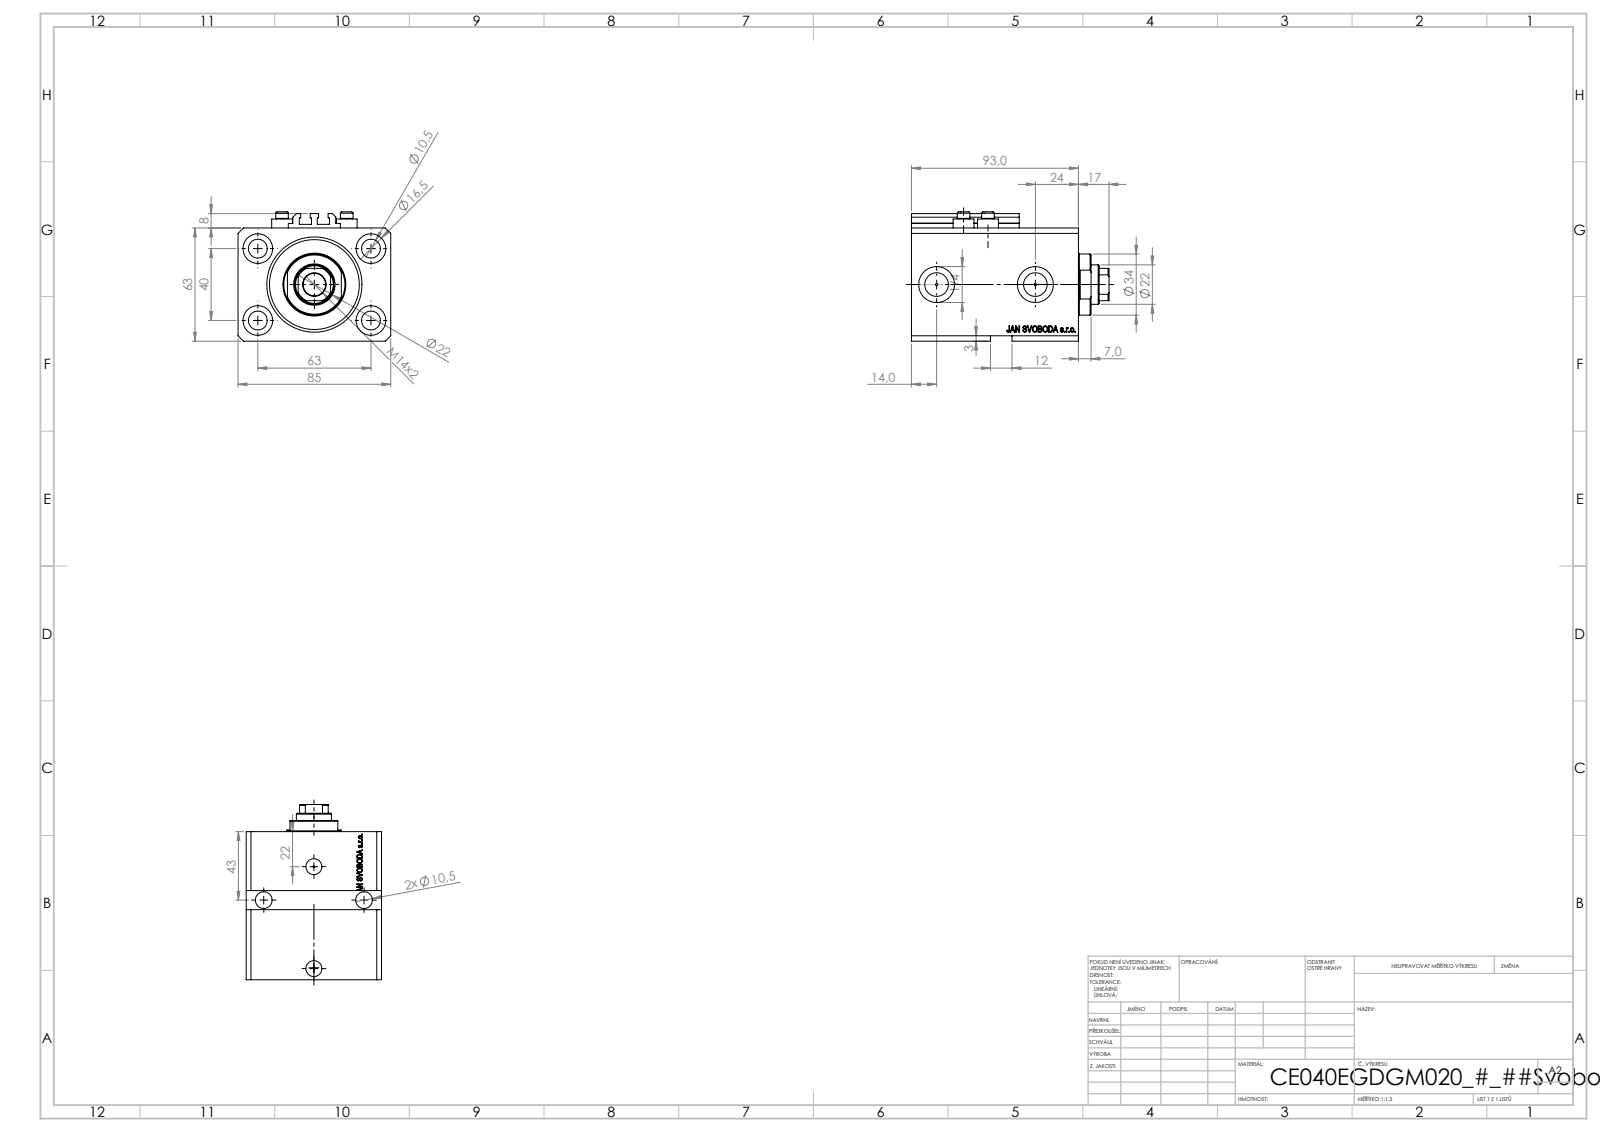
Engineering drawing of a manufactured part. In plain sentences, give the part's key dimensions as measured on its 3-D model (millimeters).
The part is named "V250CE_E_Body; V250CE_C_VCP; V250CE_VC_E; ALLEN BOLT V250CE". Its 3-D file was written by "SolidWorks 2019 (CONFIG_CONTROL_DESIGN)". It is 8 solids with 1103 faces: 539 planar, 138 cylindrical and 426 other. Overall it measures 110 by 85 by 72 millimeters. Its volume is 433 630 cubic millimeters and its surface area 96 943 square millimeters. Round holes: 6 of diameter 10.5, 4 of diameter 1.25, 4 of diameter 4, 4 of diameter 16.5, 2 of diameter 10, 2 of diameter 13.16, 2 of diameter 20, 1 of diameter 12.5, 1 of diameter 22, 1 of diameter 40, 1 of diameter 53. Round bosses or shafts: 4 of diameter 11.6, 4 of diameter 7, 1 of diameter 34. Partial cylindrical surfaces (rounded edges, fillets, slot ends): 10 of radius 0.2, 1 of radius 10.5. The main face-to-face distances are 63, 85, 93, 17, 76, 11.4, 64.6, 81.6, 3, 65. The hole center spacings are 37.31, 63, 13.6, 15.4, 24.96, 28.02, 28.43, 33.62.
